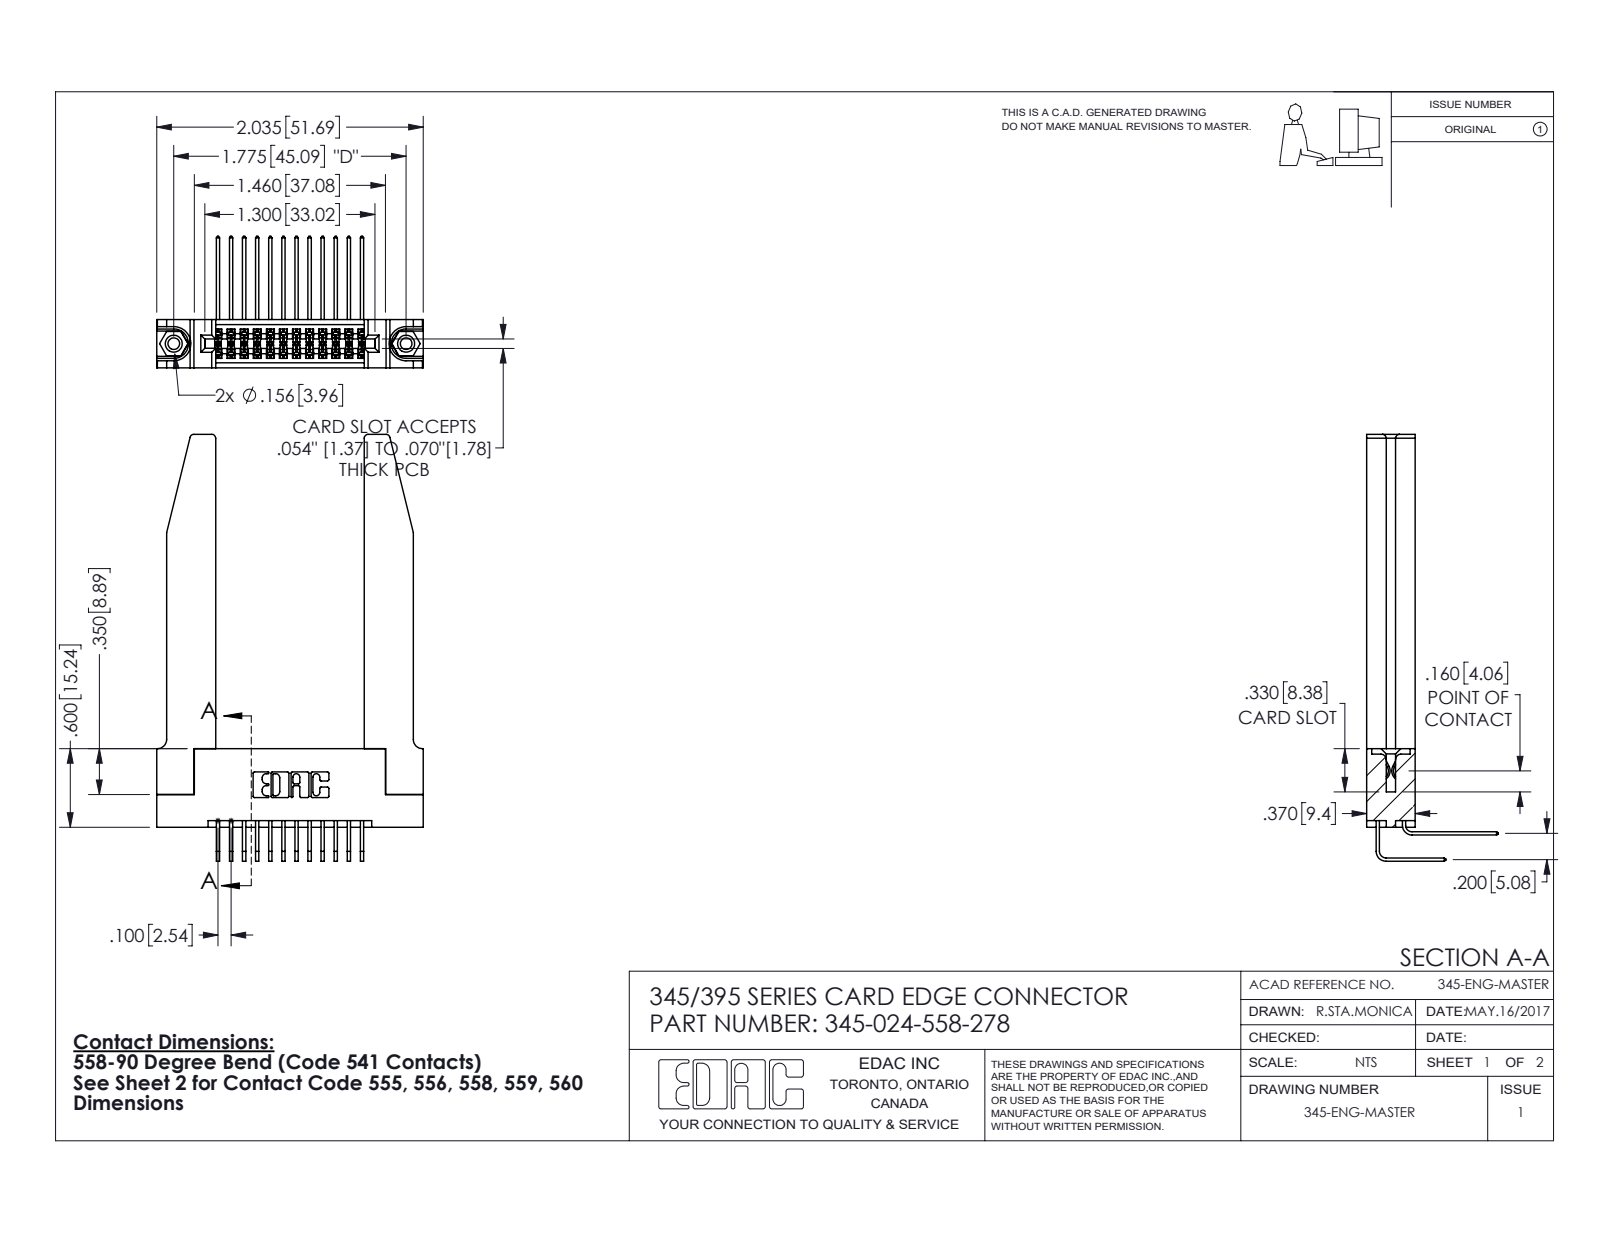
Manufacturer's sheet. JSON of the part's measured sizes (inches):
{"part_name": "345 Part_Flush Mounting Lugs - 0.156 Dia-TH; 345-292-001_558 559 Tail - 1; 345-024-558-278; 345-250-001_345-250-001-102 (+2 more)", "step_written_by": "SolidWorks 2016 (CONFIG_CONTROL_DESIGN)", "units": "inches", "bodies": {"solids": 29, "faces": 1608, "planar": 1062, "cylindrical": 494, "other": 52}, "overall_size": [3.259, 2.036, 1.005], "volume_in3": 0.772, "surface_area_in2": 21.9, "round_holes": [[0.089, 2], [0.125, 2], [0.156, 2], [0.064, 1]], "round_bosses_or_shafts": [[0.155, 2]], "partial_cylinders_radius": [[0.006, 48], [0.01, 22], [0.03, 8], [0.007, 6], [0.031, 6], [0.026, 3], [0.014, 2], [0.019, 2]], "face_to_face_distances": [0.37, 0.2, 0.072, 0.298, 0.15, 0.148, 0.077, 0.22, 1.135, 0.098], "hole_center_spacings": [0.27, 1.543, 1.775]}
